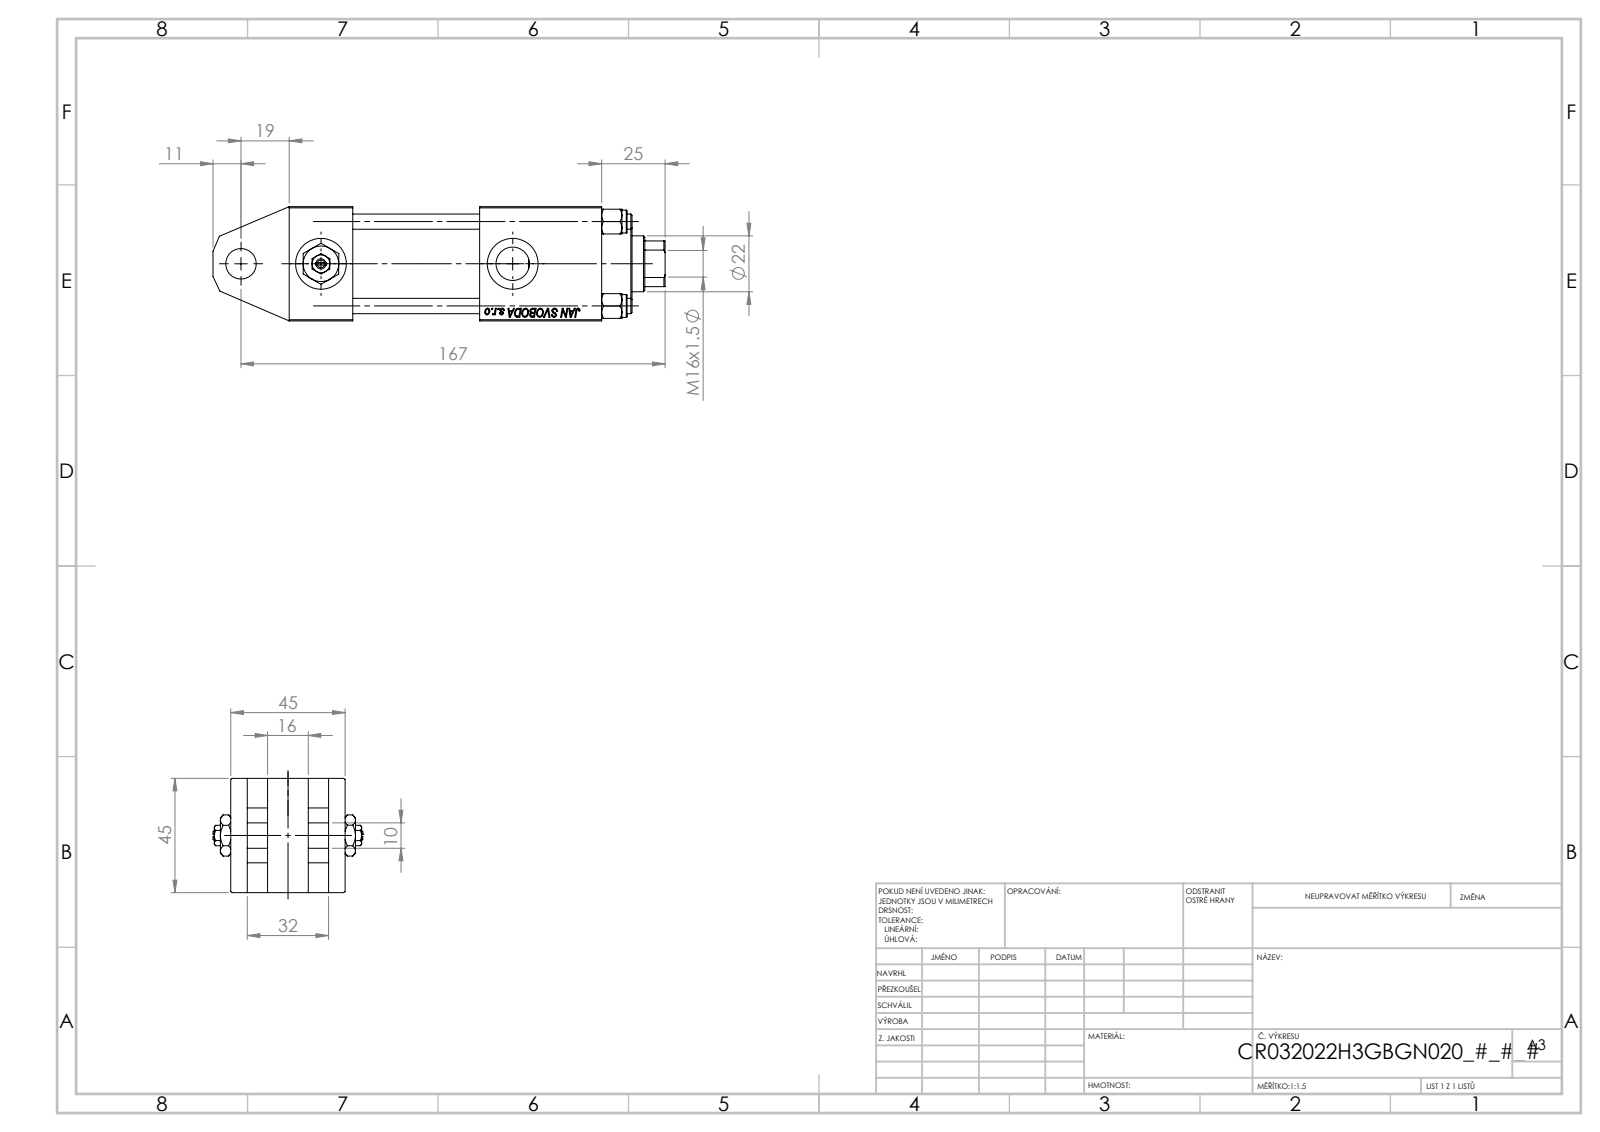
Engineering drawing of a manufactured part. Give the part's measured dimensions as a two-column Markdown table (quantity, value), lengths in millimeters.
| quantity | value |
| --- | --- |
| part name | NUT_M5_H; V215CR_TYCINKA_H; V215CR_H_Body; Zatka_pro_OIL_PORT (+2 more) |
| STEP written by | SolidWorks 2019 (CONFIG_CONTROL_DESIGN) |
| units | millimeters |
| bodies | 13 solids, 1236 faces (564 planar, 98 cylindrical, 574 other) |
| overall size | 178 × 59 × 45 |
| volume | 223 189 mm³ |
| surface area | 80 411 mm² |
| round holes (diameter × count) | 6 × 4, 2.5 × 2, 7 × 2, 13.16 × 2, 20 × 2, 10.5 × 1, 12 × 1, 22 × 1, 24 × 1, 25 × 1, 32 × 1, 33 × 1 |
| round bosses / shafts (diameter × count) | 9 × 4, 38 × 1, 34 × 1 |
| partial cylindrical surfaces (radius × count) | 10.5 × 1 |
| main face-to-face distances | 45, 8, 6.5, 38.5, 24, 14.5, 30.5, 25, 123, 50 |
| hole center spacings | 16.7, 23.48, 33.2, 35.47, 14.75, 46.95, 29.5, 31.5 |
